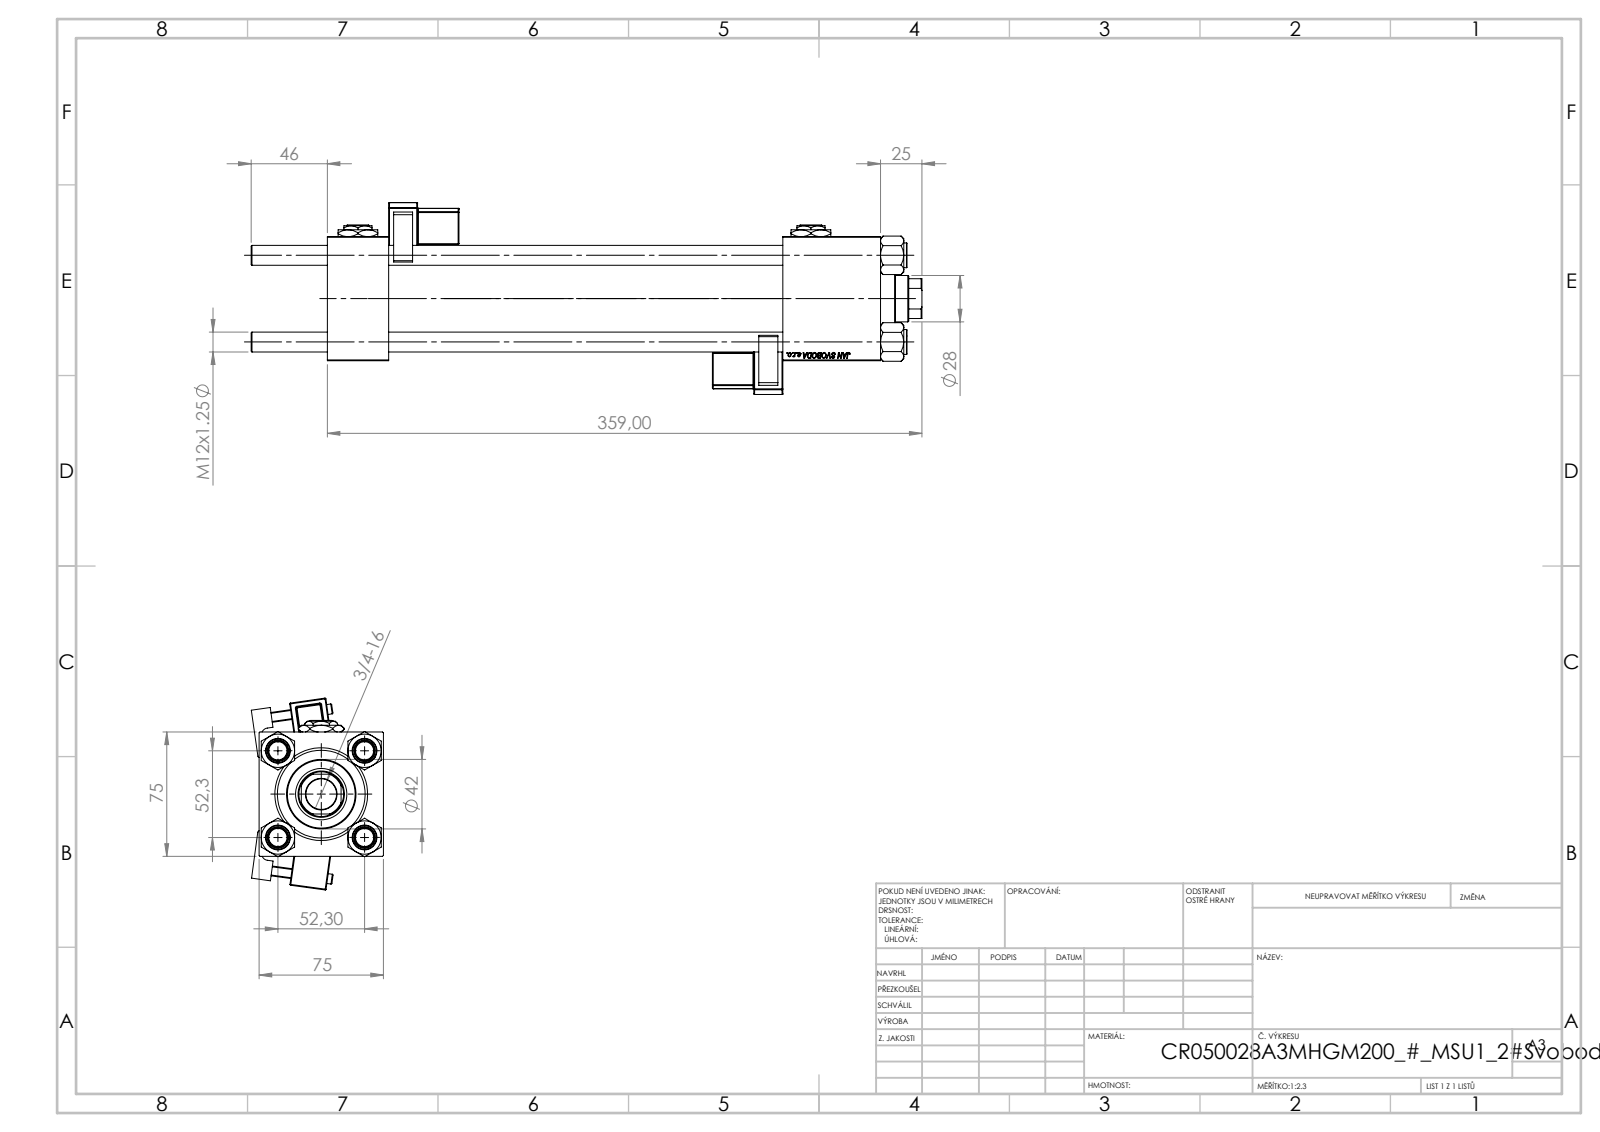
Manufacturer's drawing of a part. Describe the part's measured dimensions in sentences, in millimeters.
The part is named "CR025_012_A_0_G_A_G_M_020_+#_##_TYCINKA; V215CR_MSU; V215CR_VCP; V215CR_BODY_A (+3 more)". Its 3-D file was written by "SolidWorks 2019 (CONFIG_CONTROL_DESIGN)". It is 15 solids with 1387 faces: 625 planar, 148 cylindrical and 614 other. Overall it measures 405 by 115.75 by 79.69 millimeters. Its volume is 1 020 000 cubic millimeters and its surface area 287 053 square millimeters. Round holes: 4 of diameter 12, 2 of diameter 7, 2 of diameter 20.96, 2 of diameter 30, 1 of diameter 18.5, 1 of diameter 28, 1 of diameter 31, 1 of diameter 41, 1 of diameter 50, 1 of diameter 53. Round bosses or shafts: 4 of diameter 15, 2 of diameter 6, 1 of diameter 56, 1 of diameter 42. Partial cylindrical surfaces (rounded edges, fillets, slot ends): 48 of radius 0.5, 2 of radius 1, 2 of radius 2.5, 2 of radius 4, 1 of radius 13.5. The main face-to-face distances are 75, 37, 275, 334, 297, 238, 59, 305.3, 268.3, 30.3. The hole center spacings are 36.98, 52.3, 73.96, 273.5.
